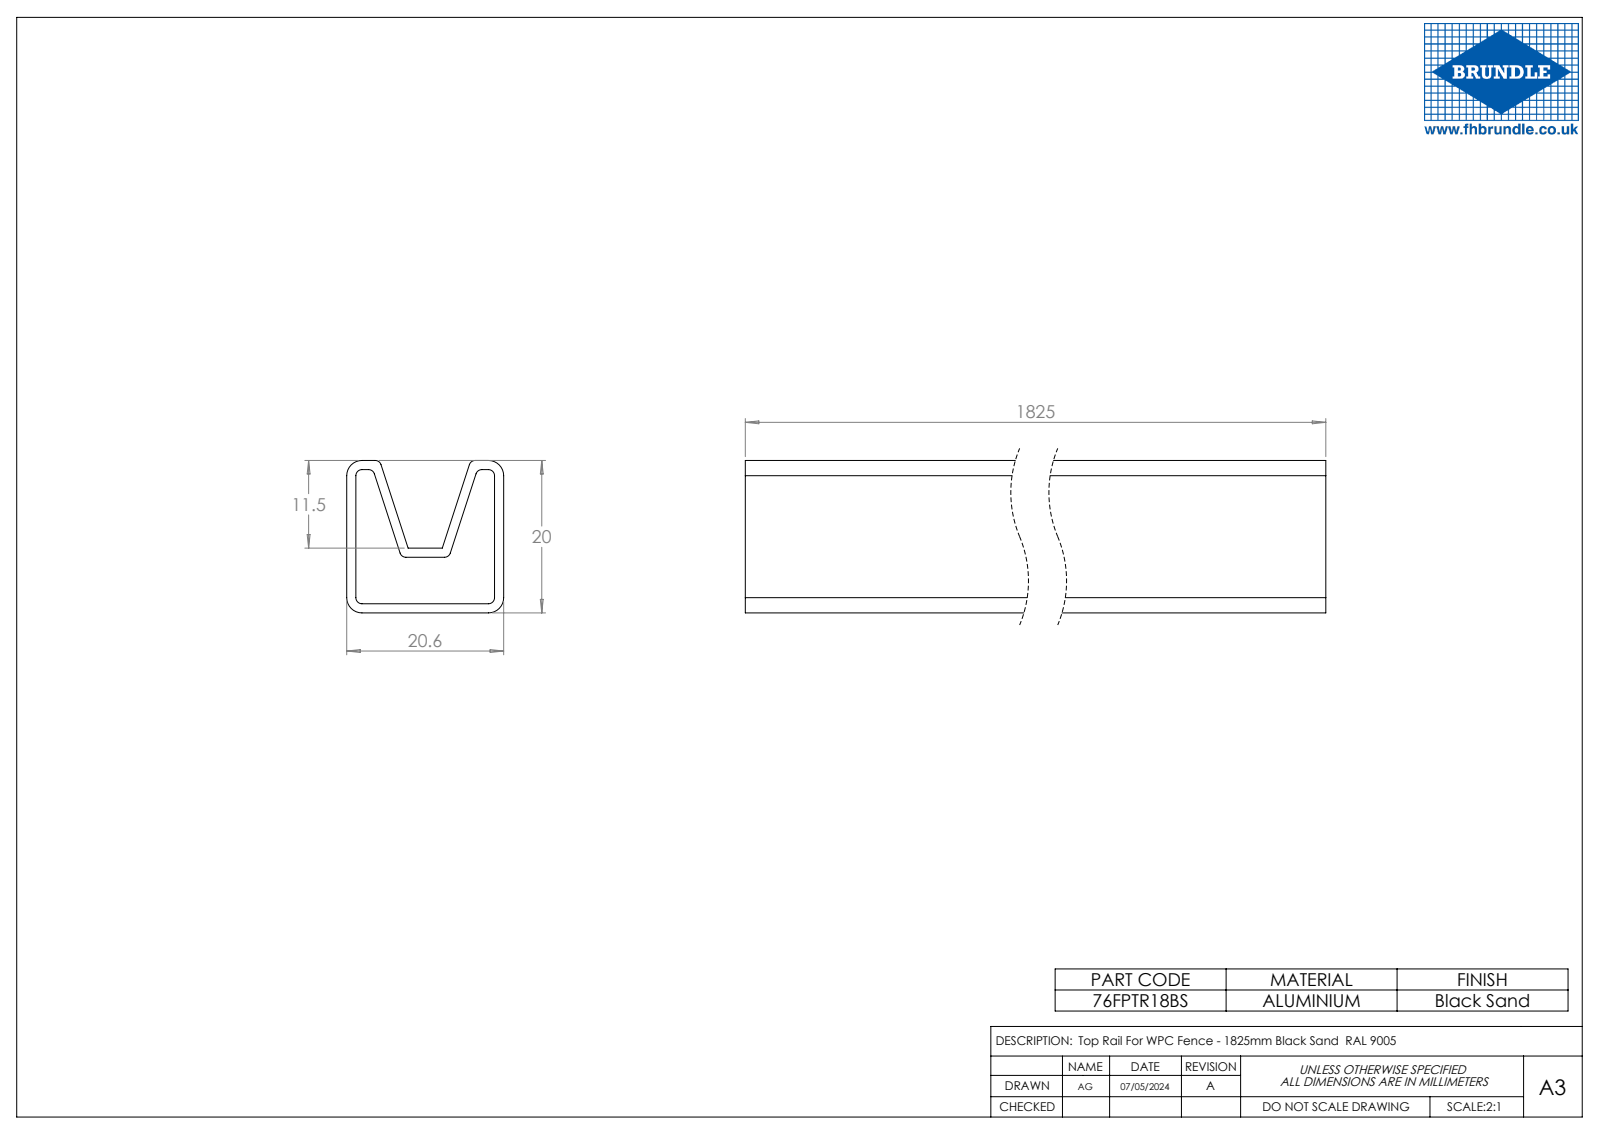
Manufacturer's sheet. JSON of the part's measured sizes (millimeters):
{"part_name": "76FPTR18BS", "step_written_by": "SolidWorks 2023 (CONFIG_CONTROL_DESIGN)", "units": "millimeters", "bodies": {"solids": 1, "faces": 32, "planar": 18, "cylindrical": 14, "other": 0}, "overall_size": [1825, 20.6, 20], "volume_mm3": 198419, "surface_area_mm2": 329577, "partial_cylinders_radius": [[0.8, 10], [2, 4]], "face_to_face_distances": [1.2, 19.4, 20.6, 18.2, 7.3, 18.8, 11.5, 6.1, 8.5, 20]}
